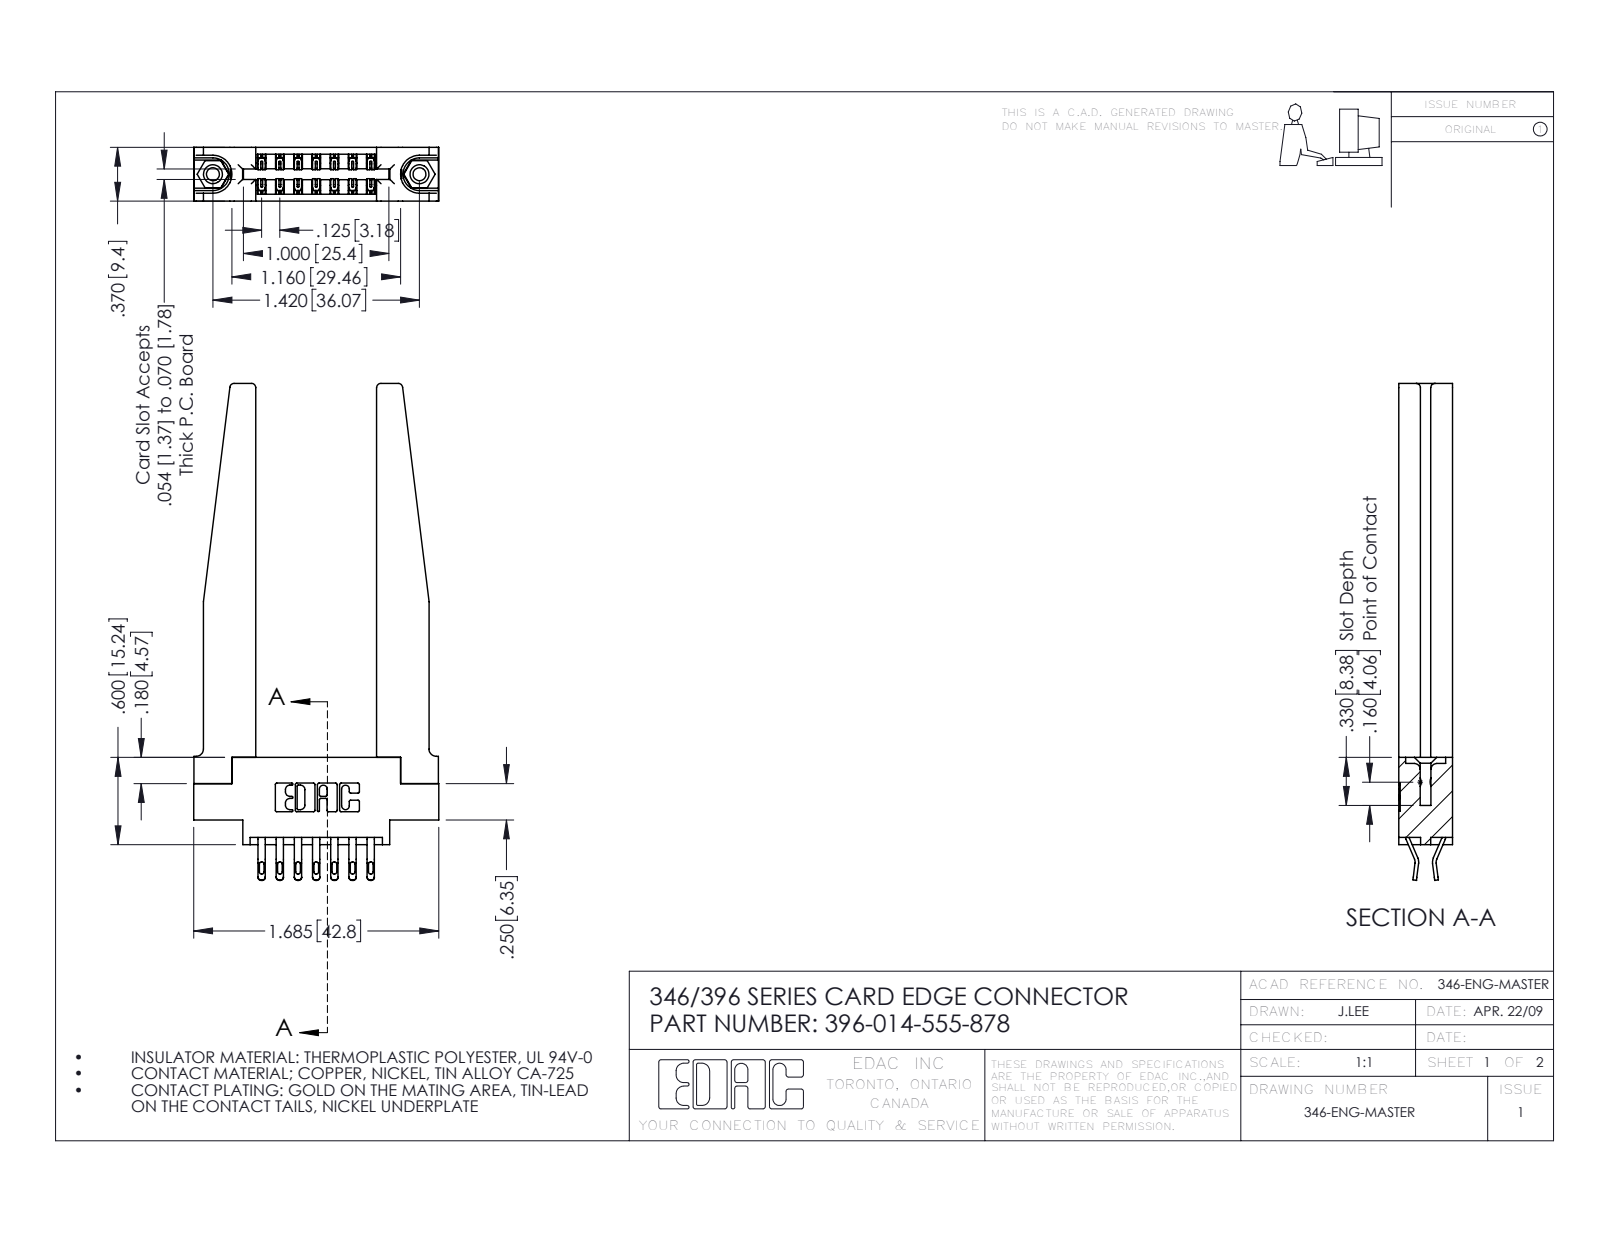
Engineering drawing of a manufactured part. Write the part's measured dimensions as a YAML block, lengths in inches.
part_name: "346 Part_0.170 Offset - 0.156 Dia-TH; 345-250-001_345-250-001-102; 346-220-078_345-220-078; 345-292-001_555 Tail (+1 more)"
step_written_by: "SolidWorks 2016 (CONFIG_CONTROL_DESIGN)"
units: inches
bodies: {solids: 19, faces: 1172, planar: 684, cylindrical: 436, other: 52}
overall_size: [3.415, 1.685, 0.37]
volume: 0.653
surface_area: 17.85
round_holes:
  - {diameter: 0.089, count: 2}
  - {diameter: 0.125, count: 2}
  - {diameter: 0.156, count: 2}
  - {diameter: 0.064, count: 1}
round_bosses_or_shafts:
  - {diameter: 0.155, count: 2}
partial_cylinders:
  - {radius: 0.016, count: 28}
  - {radius: 0.02, count: 28}
  - {radius: 0.01, count: 22}
  - {radius: 0.006, count: 21}
  - {radius: 0.03, count: 8}
  - {radius: 0.007, count: 6}
  - {radius: 0.031, count: 6}
  - {radius: 0.05, count: 4}
face_to_face_distances: [0.37, 0.15, 0.22, 0.25, 0.831, 0.148, 0.072, 0.102, 0.048, 0.322]
hole_center_spacings: [0.246, 1.217, 1.42]
